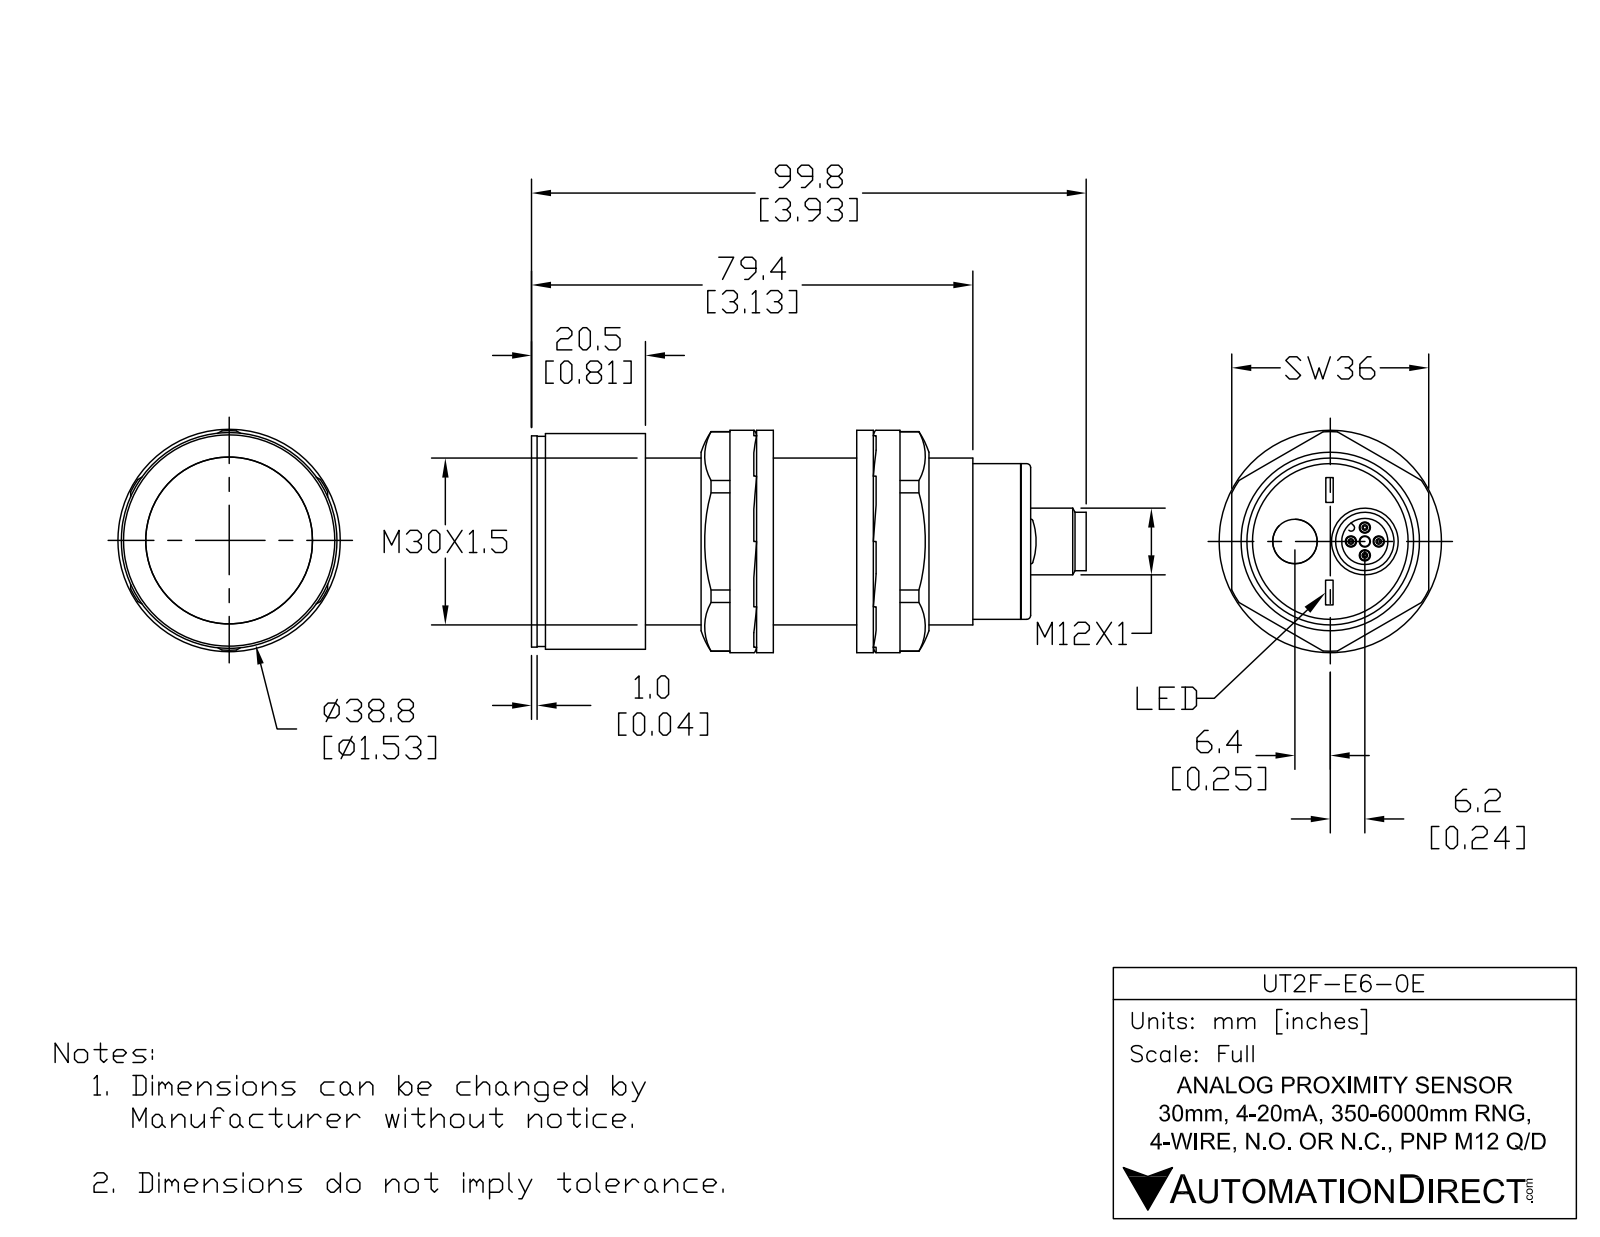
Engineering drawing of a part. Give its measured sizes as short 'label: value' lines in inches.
name: UT2F-E6-0E
written by: SolidWorks 2017 (AUTOMOTIVE_DESIGN)
unit: in
bodies: 5 solids, 108 faces (31 planar, 47 cylindrical, 30 other)
size: 3.894 × 1.528 × 1.528
volume: 4.372 in³; area: 24.88 in²
holes: 4× ⌀0.071, 1× ⌀0.315, 1× ⌀0.327, 1× ⌀0.372, 1× ⌀1.299
bosses: 4× ⌀0.039, 1× ⌀1.528, 1× ⌀1.488, 1× ⌀1.181, 1× ⌀1.102, 1× ⌀0.472, 1× ⌀0.413, 1× ⌀0.364
rounds: 2× R0.012, 1× R0.024
face distances: 3.37, 0.059, 3.429, 0.767, 0.709, 2.661, 0.059, 3.429, 0.071, 3.5
hole spacings: 0.098, 0.139, 0.197, 0.264, 0.505, 0.146, 0.245, 0.25
